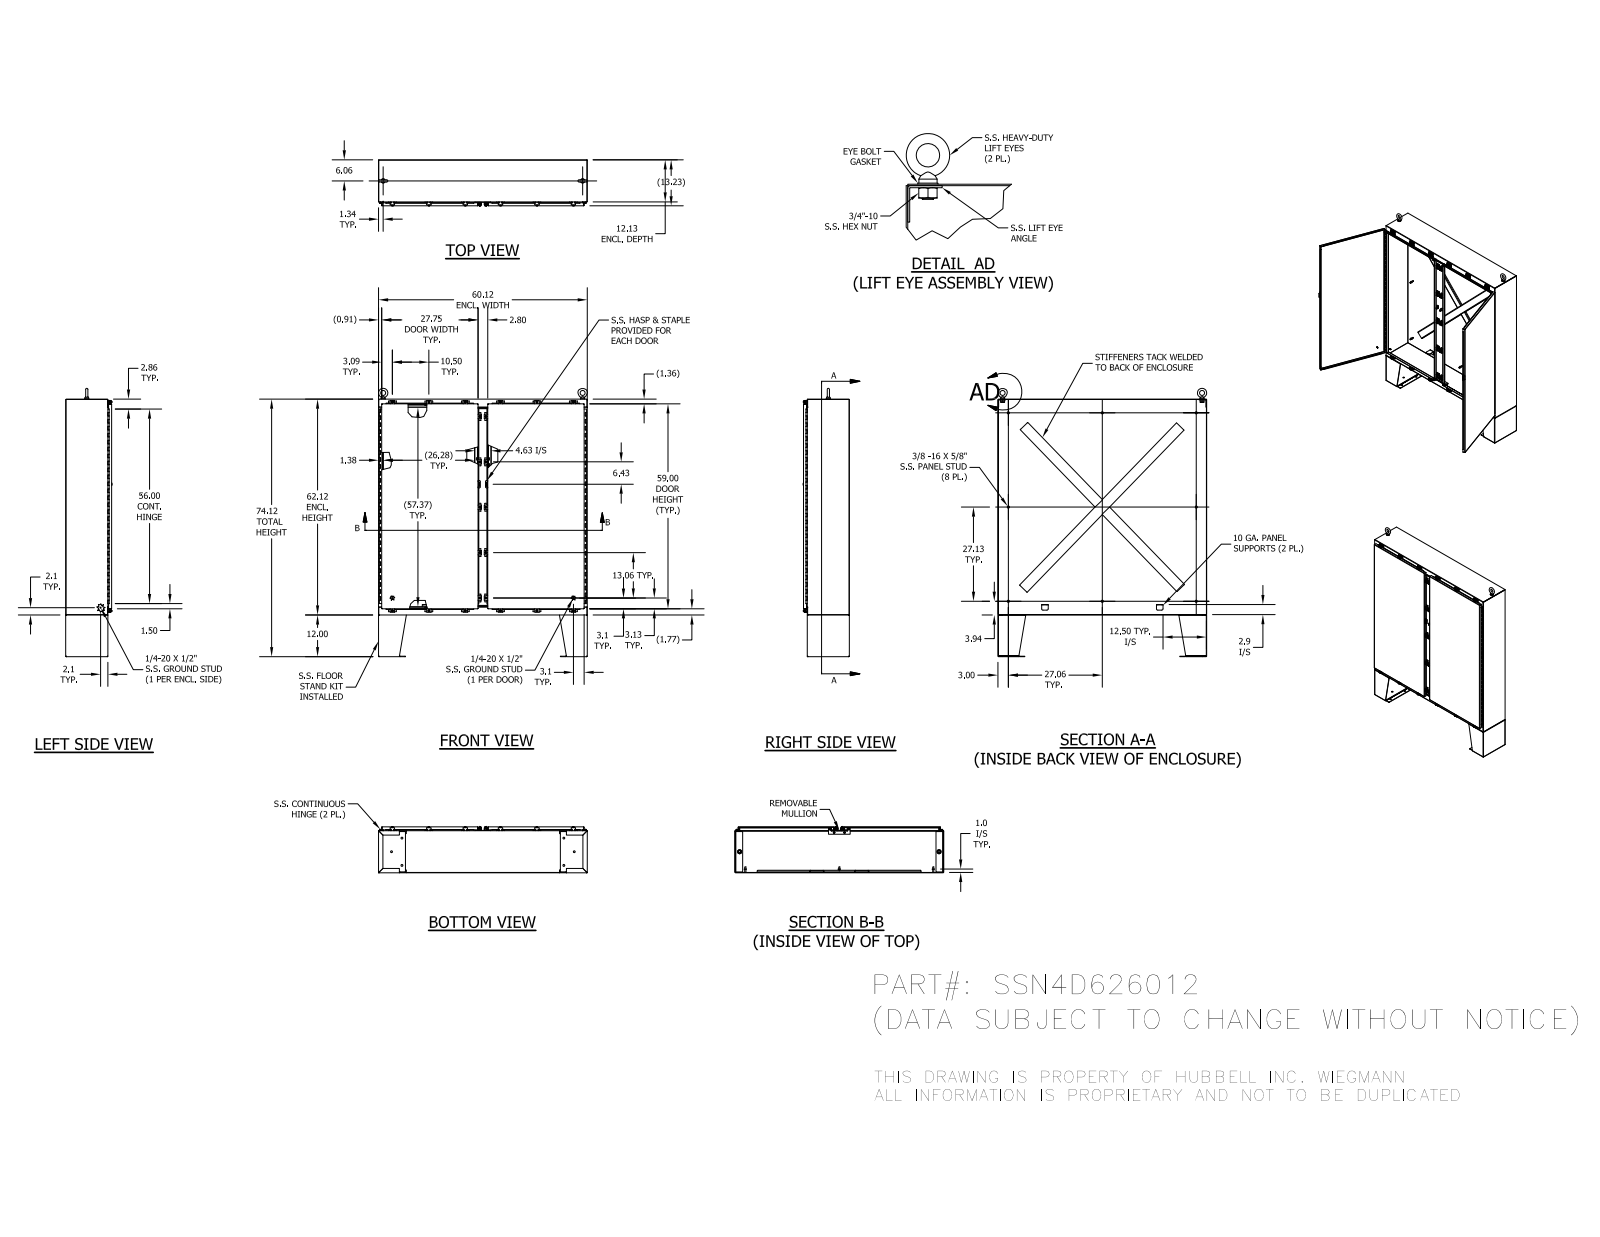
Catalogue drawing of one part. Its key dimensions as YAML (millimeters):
part_name: "38714_1; 31666_1; SSN4D62MLR_1; 316298_1 (+8 more)"
step_written_by: "SolidWorks 2014 (AUTOMOTIVE_DESIGN)"
units: millimeters
bodies: {solids: 175, faces: 6460, planar: 2572, cylindrical: 2576, other: 1312}
overall_size: [1962.1, 1527.2, 339.2]
volume: 21070000
surface_area: 17460000
round_holes:
  - {diameter: 2.8, count: 44}
  - {diameter: 5.4, count: 22}
  - {diameter: 7.1, count: 22}
  - {diameter: 7.6, count: 22}
  - {diameter: 14.3, count: 18}
  - {diameter: 9.5, count: 16}
  - {diameter: 5, count: 4}
  - {diameter: 5.1, count: 4}
  - {diameter: 7.9, count: 4}
  - {diameter: 8, count: 4}
  - {diameter: 3.6, count: 2}
  - {diameter: 4, count: 2}
round_bosses_or_shafts:
  - {diameter: 6.4, count: 29}
  - {diameter: 13.2, count: 22}
  - {diameter: 12.7, count: 22}
  - {diameter: 8.9, count: 22}
  - {diameter: 8.4, count: 10}
  - {diameter: 15.9, count: 8}
  - {diameter: 11.1, count: 4}
  - {diameter: 8.6, count: 3}
partial_cylinders:
  - {radius: 0.8, count: 246}
  - {radius: 3.2, count: 60}
  - {radius: 3.6, count: 44}
  - {radius: 6.4, count: 37}
  - {radius: 1.6, count: 32}
  - {radius: 0.8, count: 24}
  - {radius: 2.5, count: 22}
  - {radius: 0.4, count: 16}
face_to_face_distances: [2.4, 333.6, 331.2, 336, 305.6, 28, 1524.8, 1575.6, 3.2, 308]
hole_center_spacings: [266.7, 1520.5, 22.3, 1535.4, 1540.2, 1547.3, 770, 246.2]
